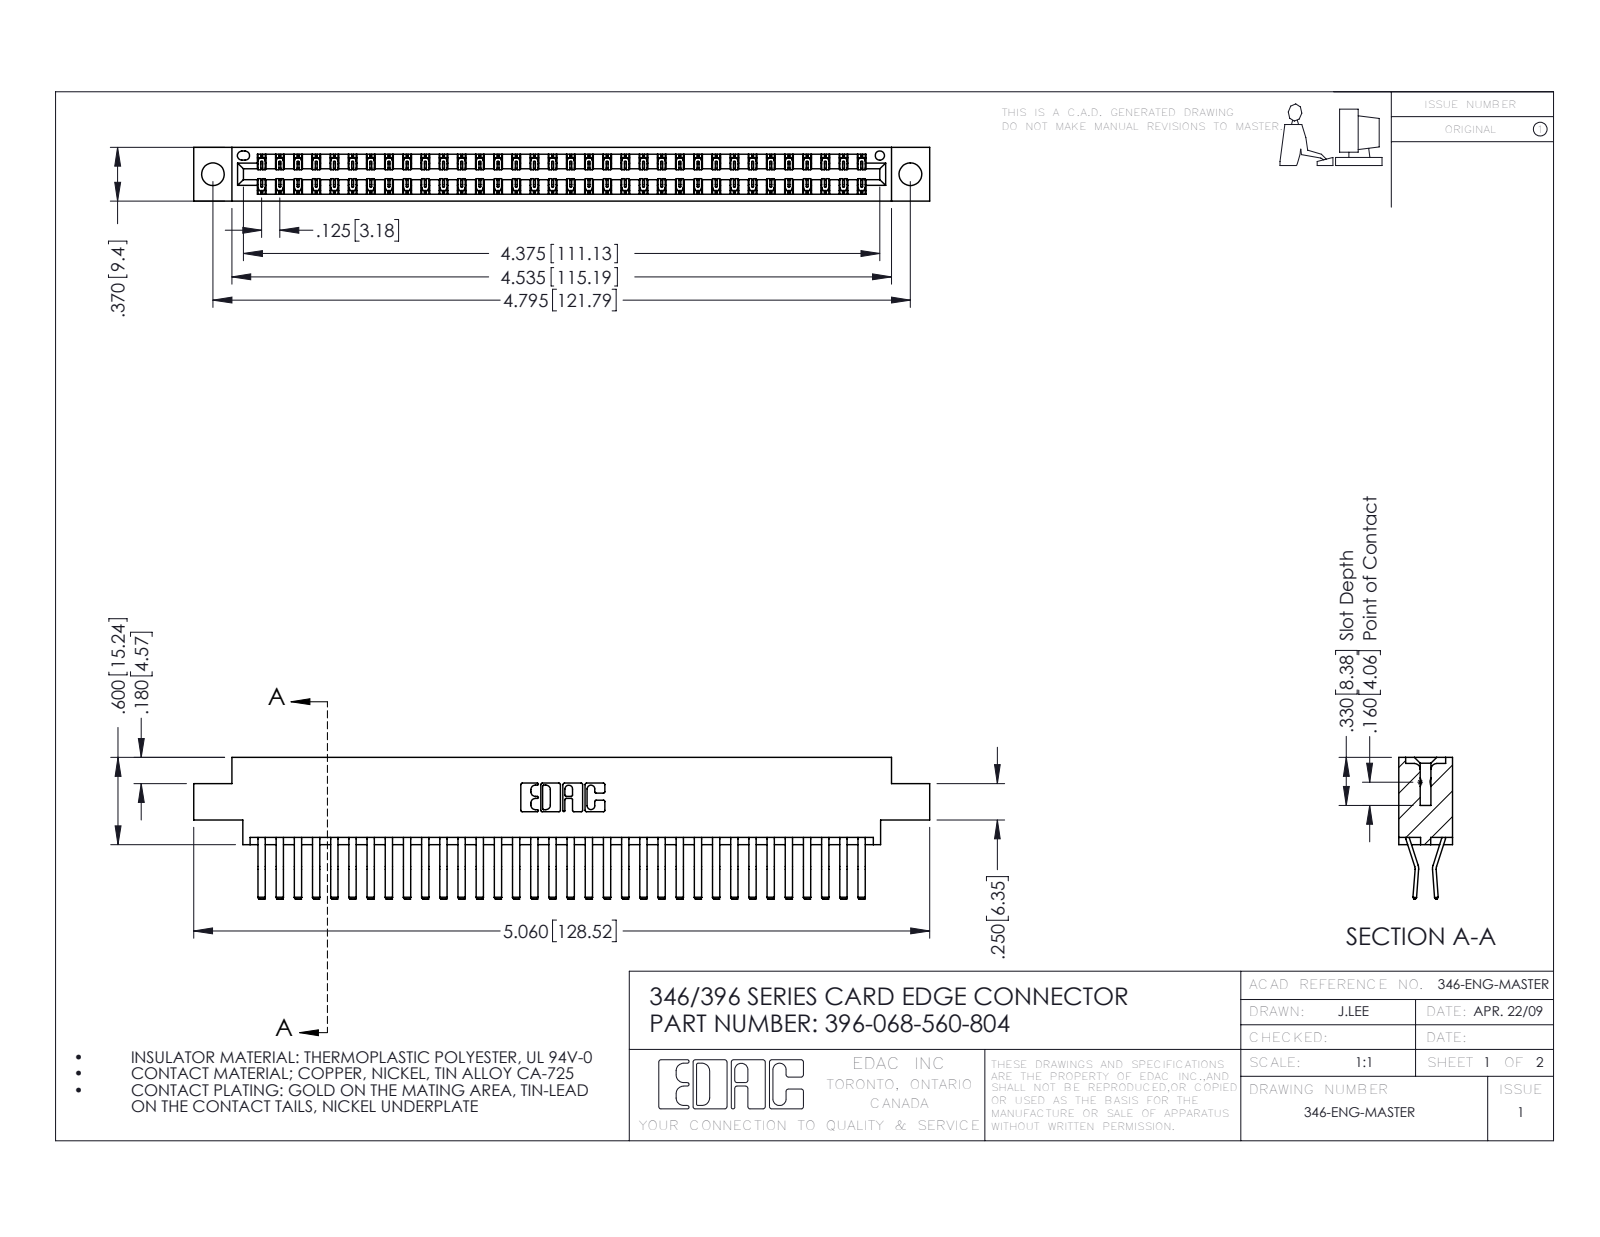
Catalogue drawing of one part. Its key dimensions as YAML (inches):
part_name: "346 Part_0.170 Offset - 0.156 Dia-TH; 396-068-560-804; 345-292-001_560 Tail"
step_written_by: "SolidWorks 2016 (CONFIG_CONTROL_DESIGN)"
units: inches
bodies: {solids: 69, faces: 3798, planar: 2460, cylindrical: 1338, other: 0}
overall_size: [5.06, 0.975, 0.37]
volume: 0.773
surface_area: 28.64
round_holes:
  - {diameter: 0.156, count: 2}
  - {diameter: 0.064, count: 1}
partial_cylinders:
  - {radius: 0.006, count: 102}
  - {radius: 0.01, count: 22}
  - {radius: 0.007, count: 6}
  - {radius: 0.031, count: 6}
  - {radius: 0.026, count: 3}
  - {radius: 0.01, count: 2}
  - {radius: 0.014, count: 2}
  - {radius: 0.022, count: 2}
face_to_face_distances: [0.048, 0.322, 0.37, 0.025, 0.25, 0.072, 0.298, 0.275, 0.148, 0.222]
hole_center_spacings: [0.246, 4.587, 4.795]
